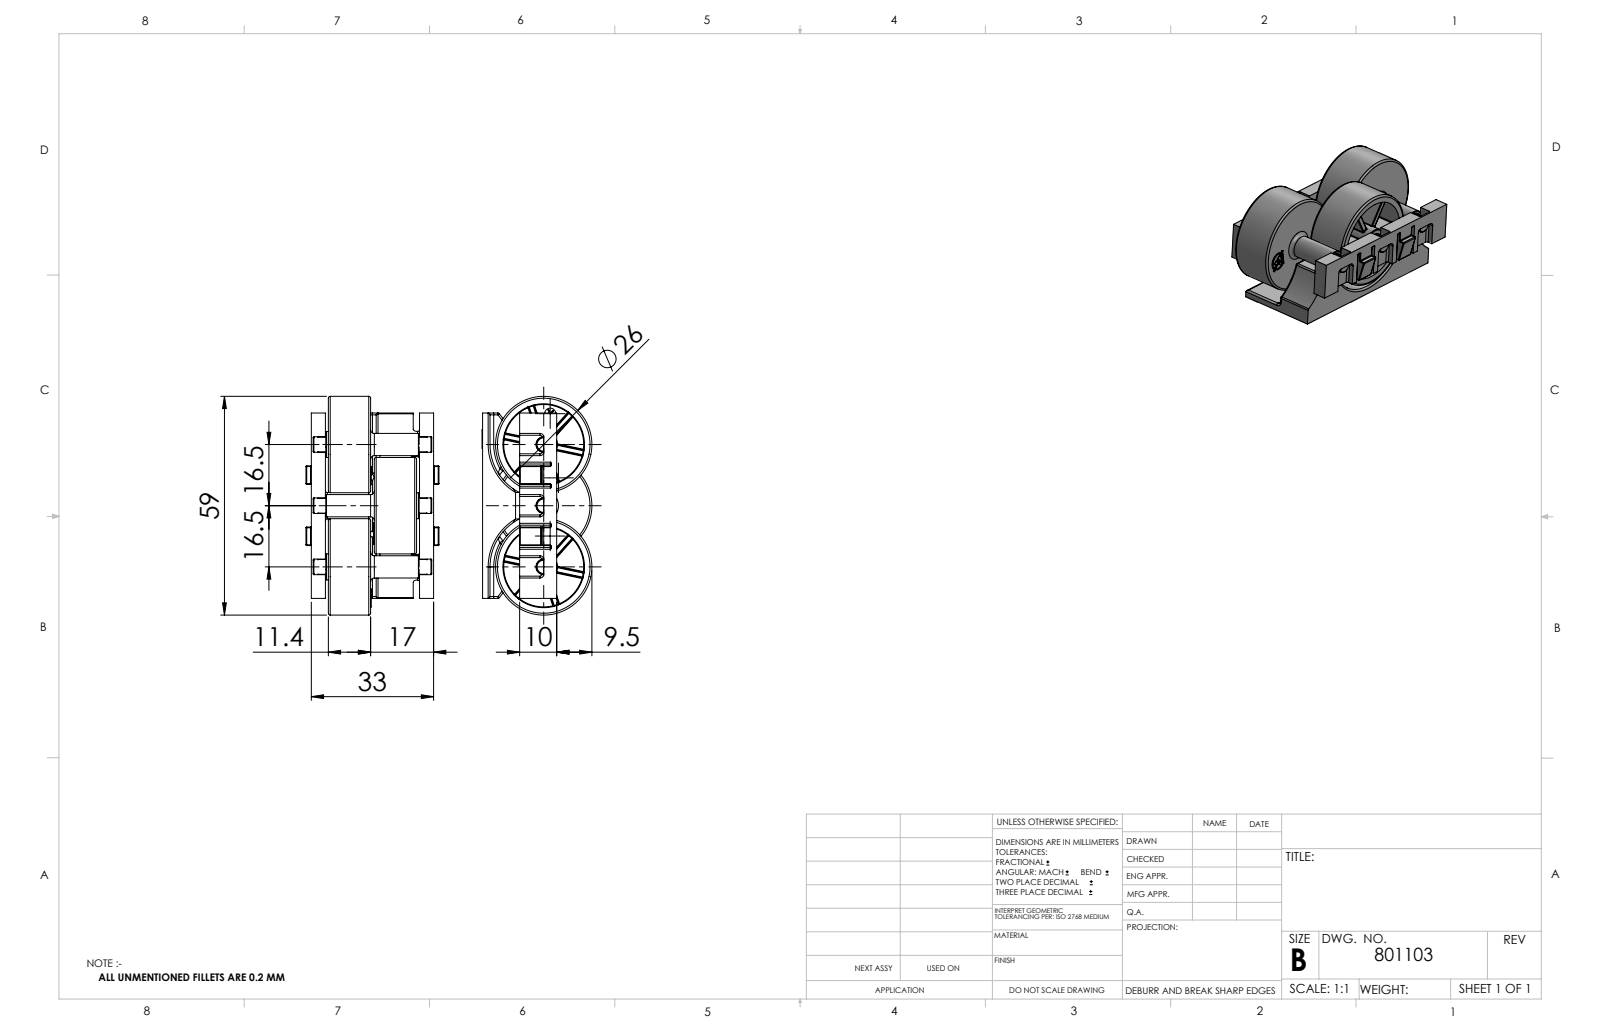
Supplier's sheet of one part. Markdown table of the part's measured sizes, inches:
| quantity | value |
| --- | --- |
| part name | 801103_c_1 |
| STEP written by | SolidWorks 2014 (CONFIG_CONTROL_DESIGN) |
| units | inches |
| bodies | 7 solids, 1557 faces (653 planar, 438 cylindrical, 466 other) |
| overall size | 2.323 × 1.413 × 1.167 |
| volume | 1.131 in³ |
| surface area | 32.61 in² |
| round holes (diameter × count) | 0.165 × 3, 0.866 × 3 |
| round bosses / shafts (diameter × count) | 1.024 × 3, 0.276 × 3, 0.236 × 3, 0.157 × 3, 0.118 × 3, 0.197 × 1 |
| partial cylindrical surfaces (radius × count) | 0.008 × 184, 0.02 × 51, 0.039 × 10, 0.012 × 6, 0.571 × 5, 0.689 × 5, 0.089 × 3, 0.099 × 3 |
| main face-to-face distances | 0.039, 0.079, 0.059, 0.52, 0.48, 0.559, 0.709, 0.394, 0.413, 0.441 |
| hole center spacings | 0.65, 1.299 |
